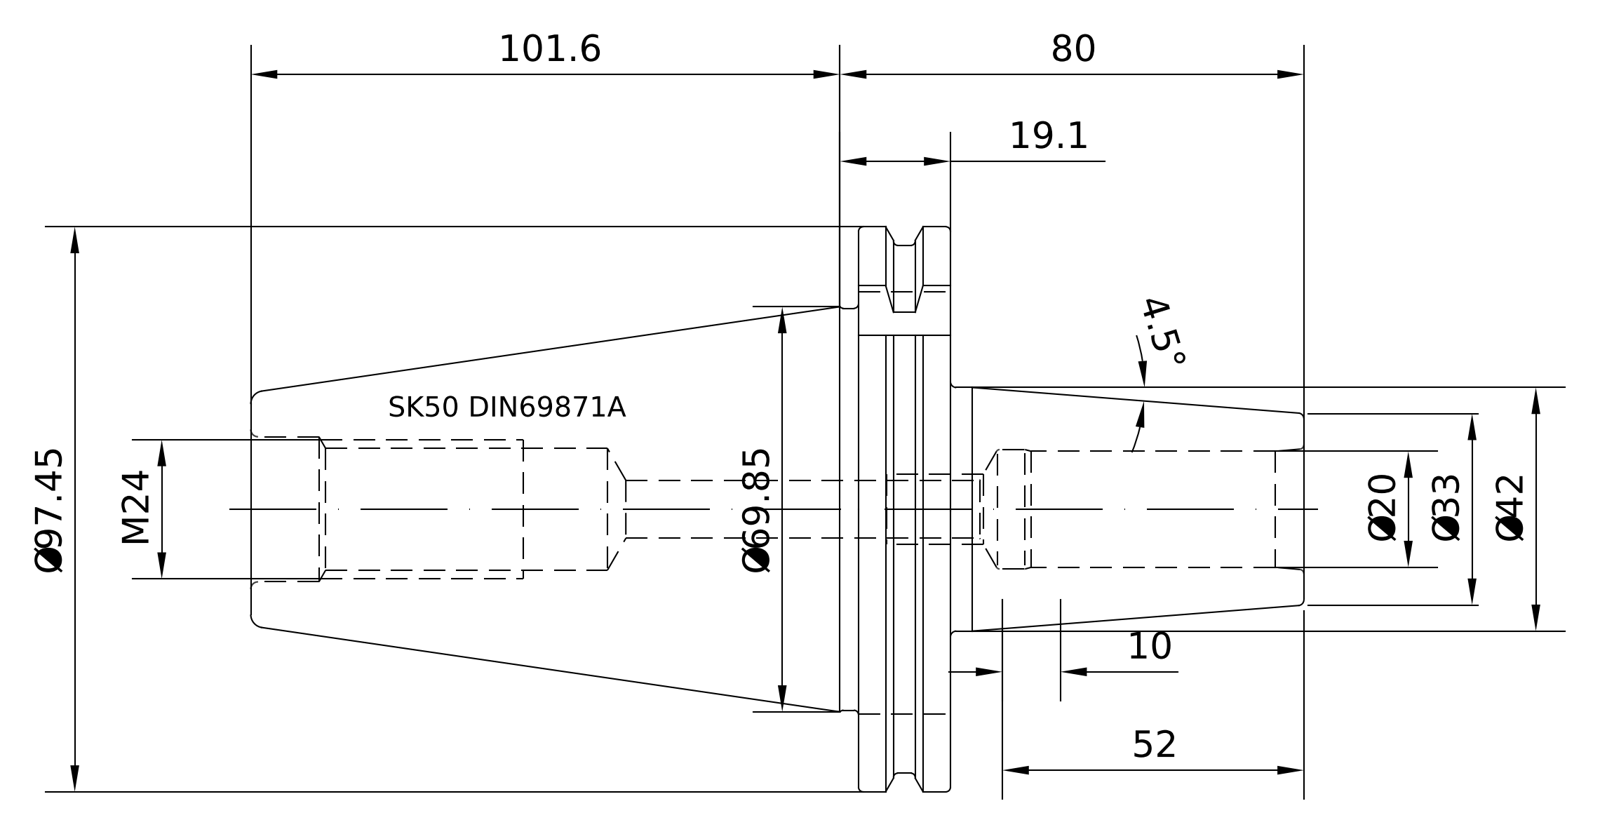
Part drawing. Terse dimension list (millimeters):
name: 50-440-20
written by: PRO/ENGINEER BY PARAMETRIC TECHNOLOGY CORPORATION, 2010430 (CONFIG_CONTROL_DESIGN)
unit: mm
bodies: 1 solid, 93 faces (21 planar, 24 cylindrical, 48 other)
size: 181.6 × 97.47 × 94
volume: 391 689 mm³; area: 52 540 mm²
holes: 1× ⌀20, 1× ⌀20.75, 1× ⌀25.01, 1× ⌀25.7
bosses: 1× ⌀91, 1× ⌀69.15, 1× ⌀42, 1× ⌀24.01
rounds: 1× R1.75, 1× R48.74
face distances: 15.85, 76.8, 60.95, 72.8, 104.8, 120.65, 181.6, 129.6, 24.8, 8.95
